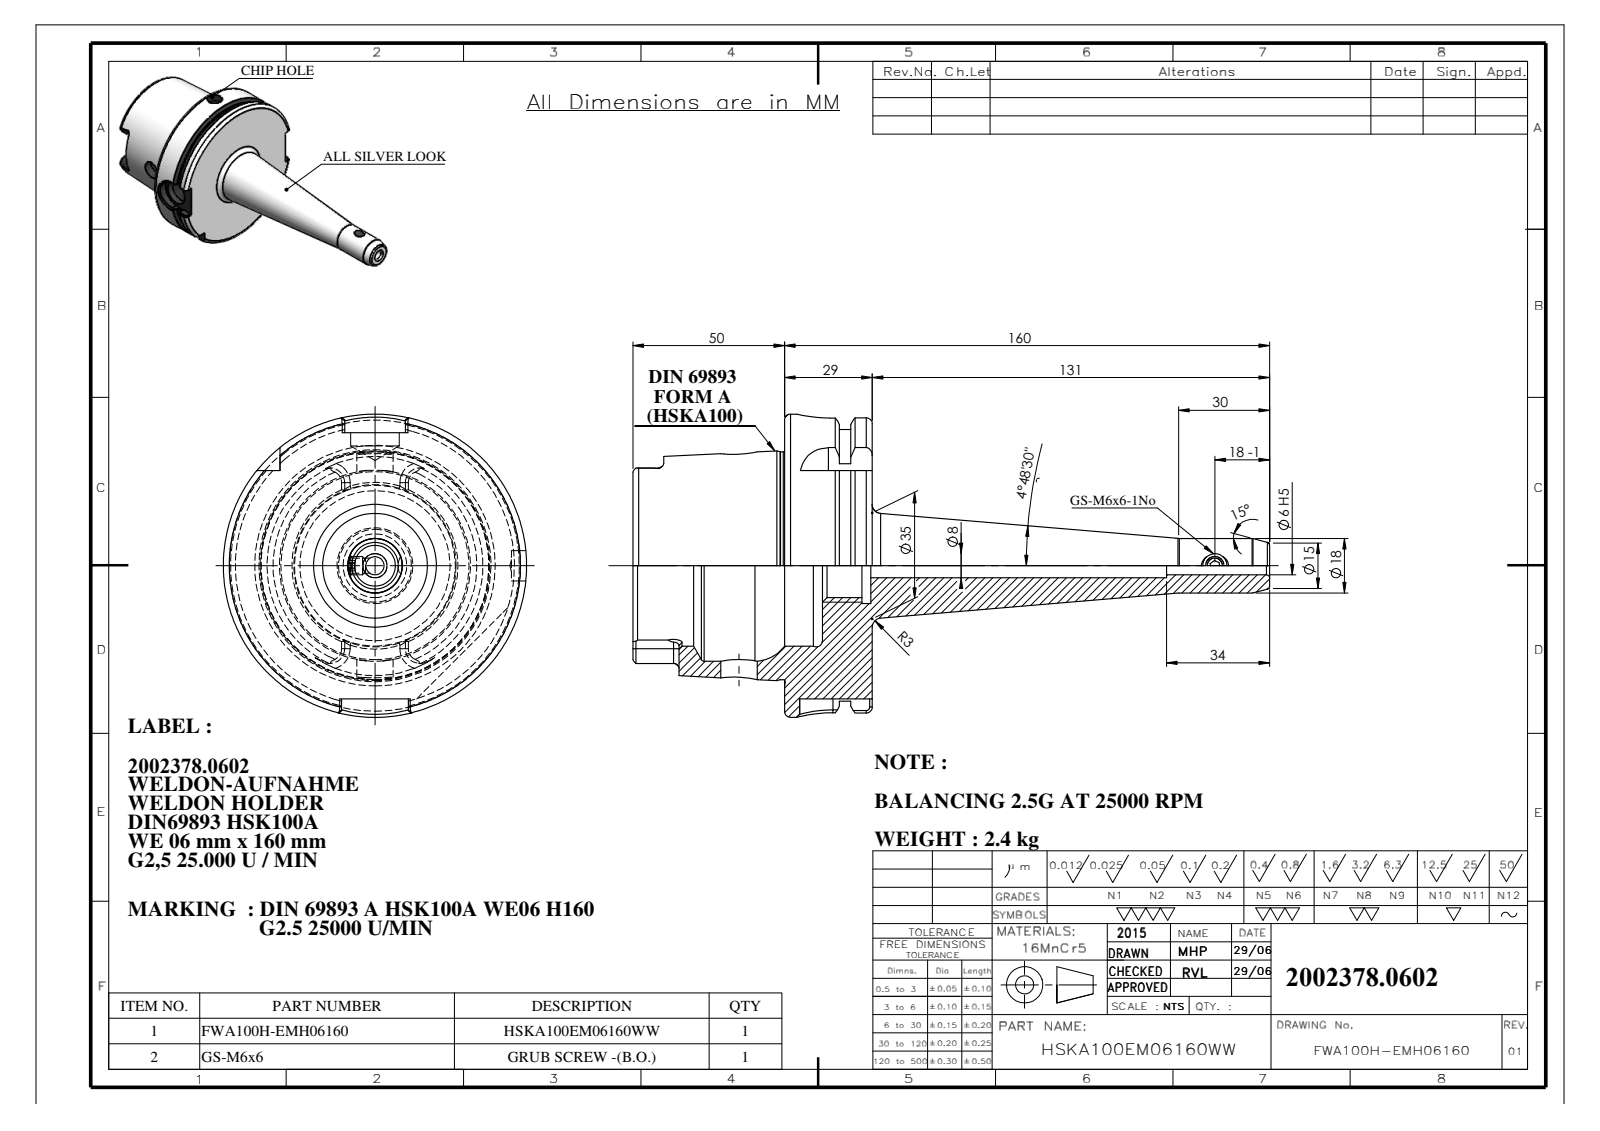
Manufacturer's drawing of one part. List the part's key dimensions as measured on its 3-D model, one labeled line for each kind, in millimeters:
Part name (STEP PRODUCT): 91100A-WE806160; HSKA100EM06160WW; M6X6_DIN 913 - M6 x 6-N
STEP written by: SolidWorks 2018 (CONFIG_CONTROL_DESIGN)
Units: millimetres
Bodies: 2 solids, 205 faces (62 planar, 56 cylindrical, 87 other)
Overall size (bounding box): 210 × 100 × 100
Volume: 311 483 mm³ · Surface area: 62 430 mm²
Round holes (diameter × count): ⌀8 ×2, ⌀5 ×1, ⌀6 ×1, ⌀10 ×1, ⌀12 ×1, ⌀16 ×1, ⌀21 ×1, ⌀25 ×1, ⌀53 ×1, ⌀63 ×1
Round bosses / shafts (diameter × count): ⌀100 ×1, ⌀92 ×1, ⌀75.16 ×1, ⌀18 ×1, ⌀6 ×1
Partial cylindrical surfaces — rounded edges, fillets, slot ends (radius × count): R1.8 ×6, R4.88 ×4, R10 ×2, R11 ×1
Main face-to-face distances: 28.95, 12.5, 16.45, 50, 62.5, 78.95, 78.5, 28.5, 16, 0.45
Hole centre spacings: 30, 135
